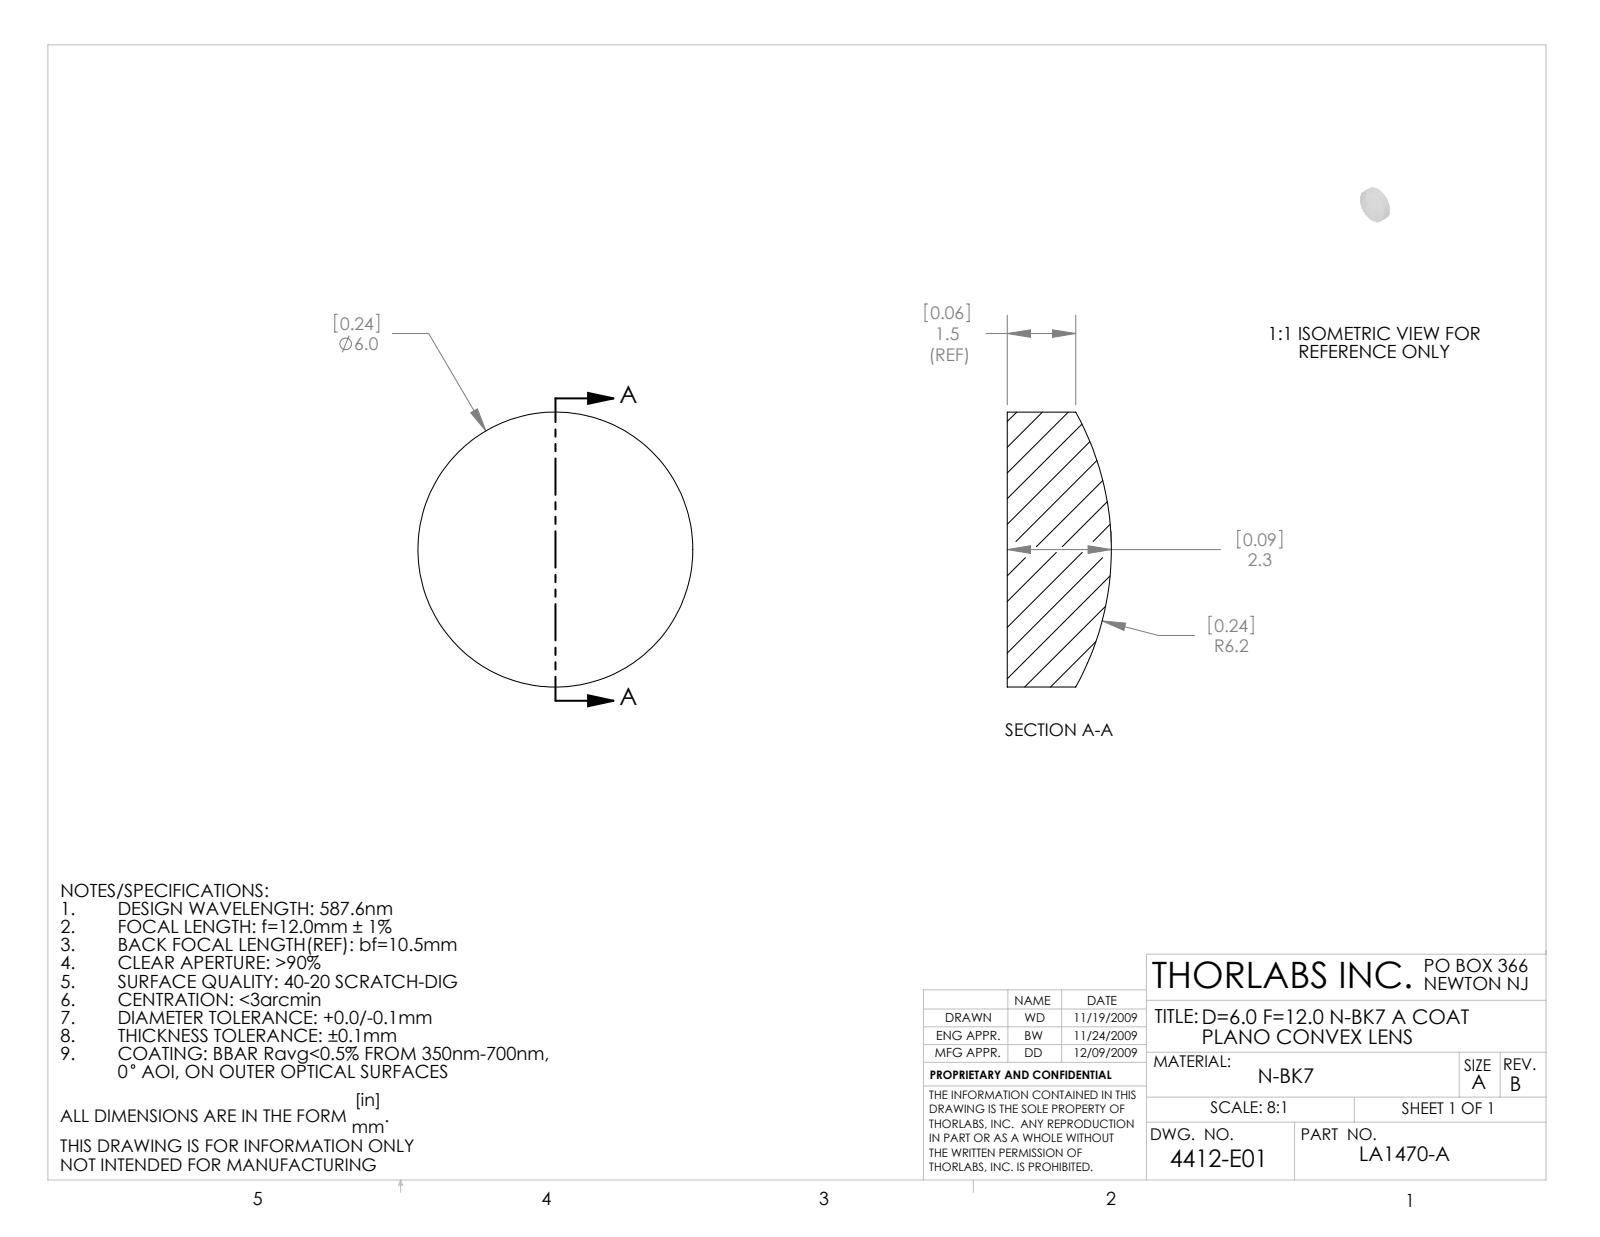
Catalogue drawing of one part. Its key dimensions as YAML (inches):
part_name: "4412-E0W"
step_written_by: "SolidWorks 2009 (AUTOMOTIVE_DESIGN)"
units: inches
bodies: {solids: 1, faces: 5, planar: 1, cylindrical: 2, other: 2}
overall_size: [0.236, 0.236, 0.089]
volume: 0.003
surface_area: 0.13
round_bosses_or_shafts:
  - {diameter: 0.236, count: 1}
